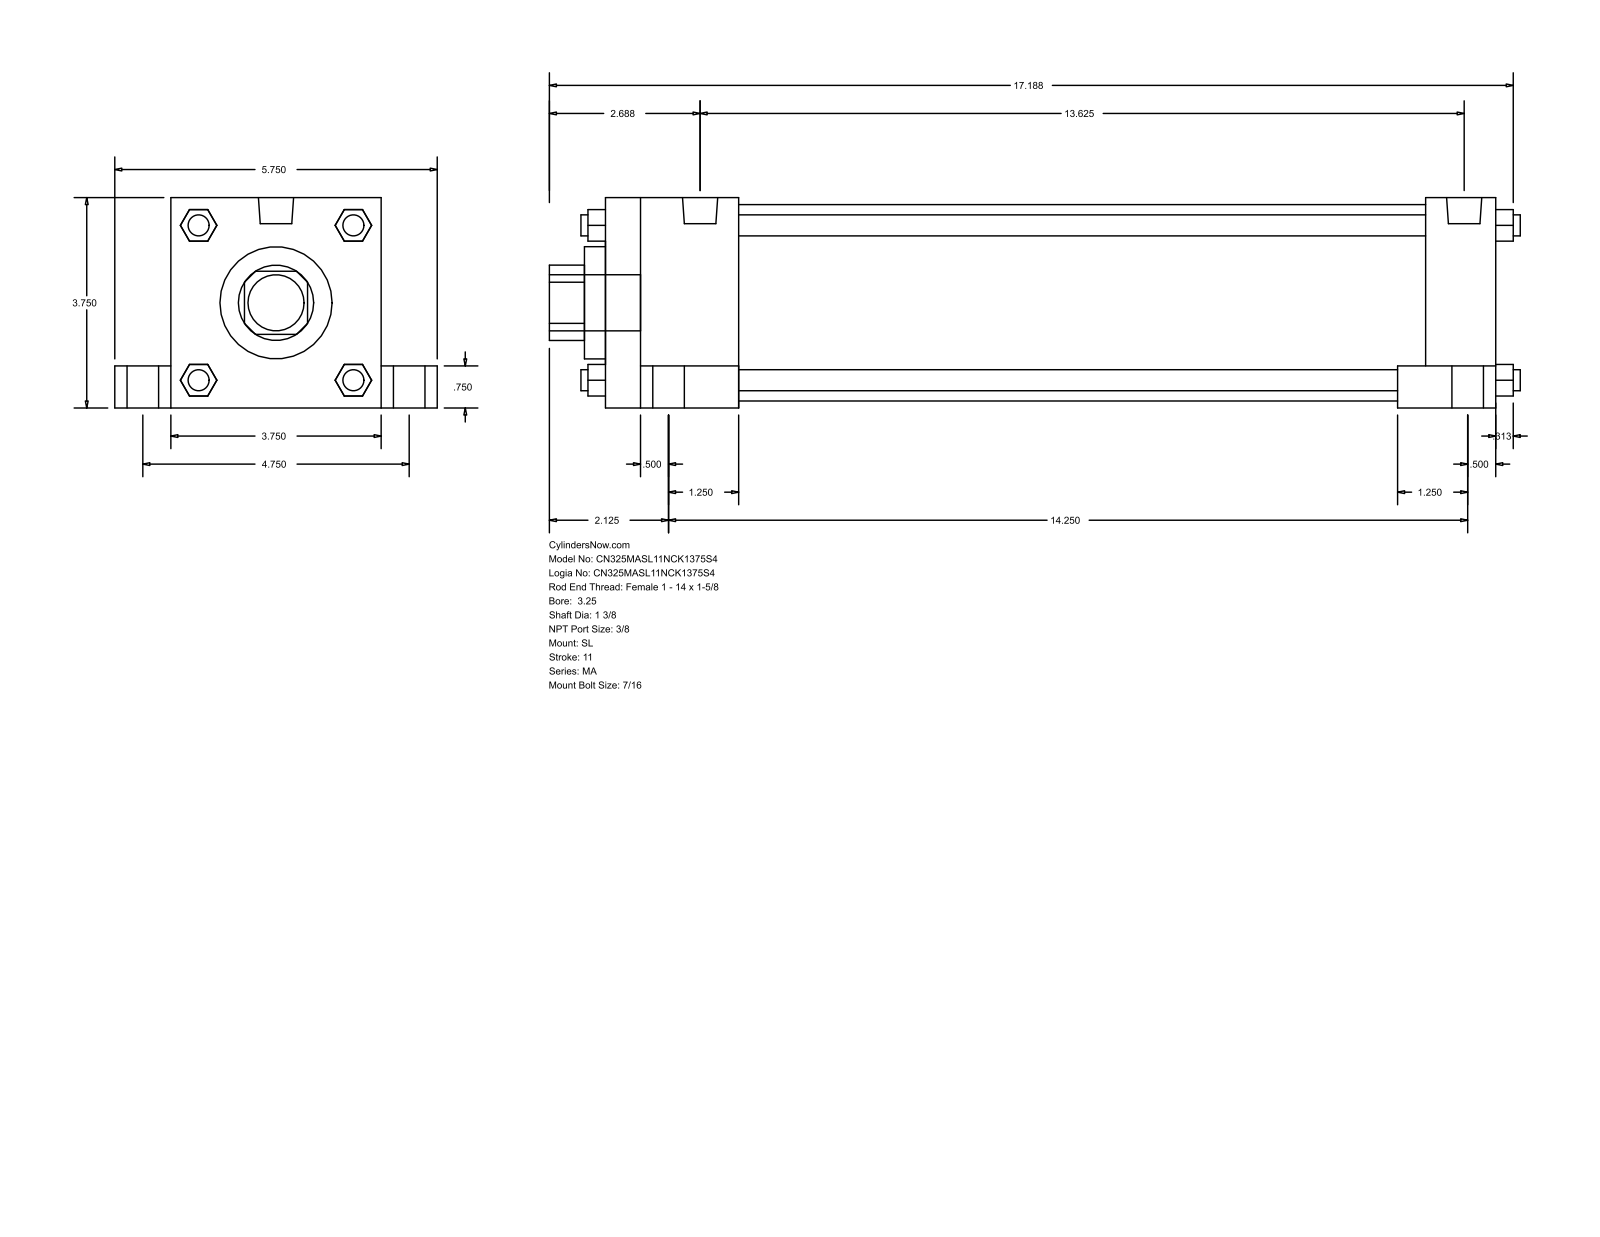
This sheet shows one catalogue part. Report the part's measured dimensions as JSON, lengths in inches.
{"part_name": "MA_SL__0325_1.375", "step_written_by": "GSSL Pune (CONFIG_CONTROL_DESIGN)", "units": "inches", "bodies": {"solids": 0, "faces": 148, "planar": 112, "cylindrical": 36, "other": 0}, "overall_size": [17.313, 5.75, 3.75], "round_holes": [[1.375, 1], [2, 1], [3.5, 1]], "round_bosses_or_shafts": [[0.813, 4], [0.563, 4], [0.437, 4], [0.375, 4], [0.627, 2], [1, 1]], "partial_cylinders_radius": [[0.672, 1]], "face_to_face_distances": [3.75, 15.875, 1, 4.75, 14.625, 1.25, 2.375, 12.25, 13.5, 0.75]}
